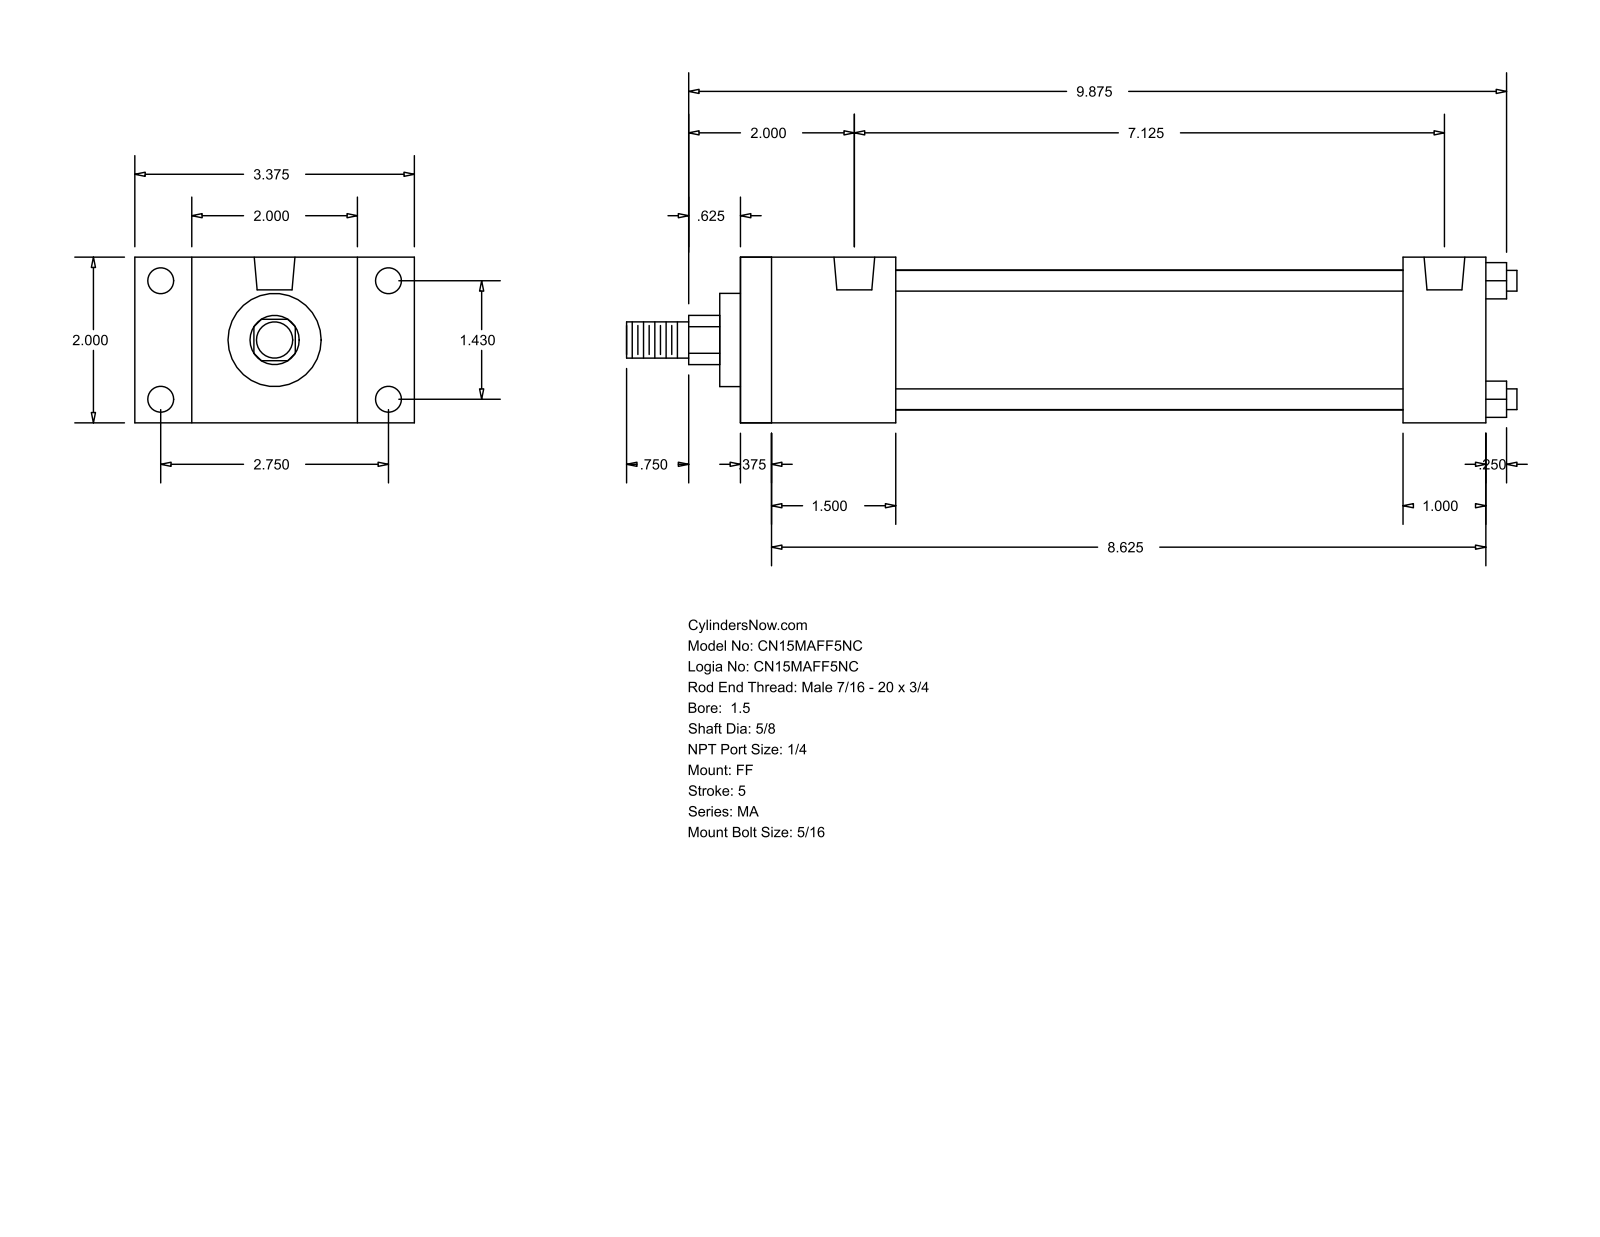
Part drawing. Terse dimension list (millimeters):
name: MA_FF__0150_0.625
written by: GSSL Pune (CONFIG_CONTROL_DESIGN)
unit: mm
bodies: 0 solids, 92 faces (64 planar, 28 cylindrical, 0 other)
size: 273.05 × 85.72 × 50.8
holes: 8× ⌀7.94, 2× ⌀12.49
bosses: 4× ⌀6.35, 1× ⌀42.93, 1× ⌀28.57, 1× ⌀15.88, 1× ⌀11.11
rounds: 1× R7.54
face distances: 50.8, 228.59, 219.07, 9.52, 25.4, 47.62, 203.19, 38.1, 193.67, 155.57
hole spacings: 36.32, 69.84, 78.72, 180.98
